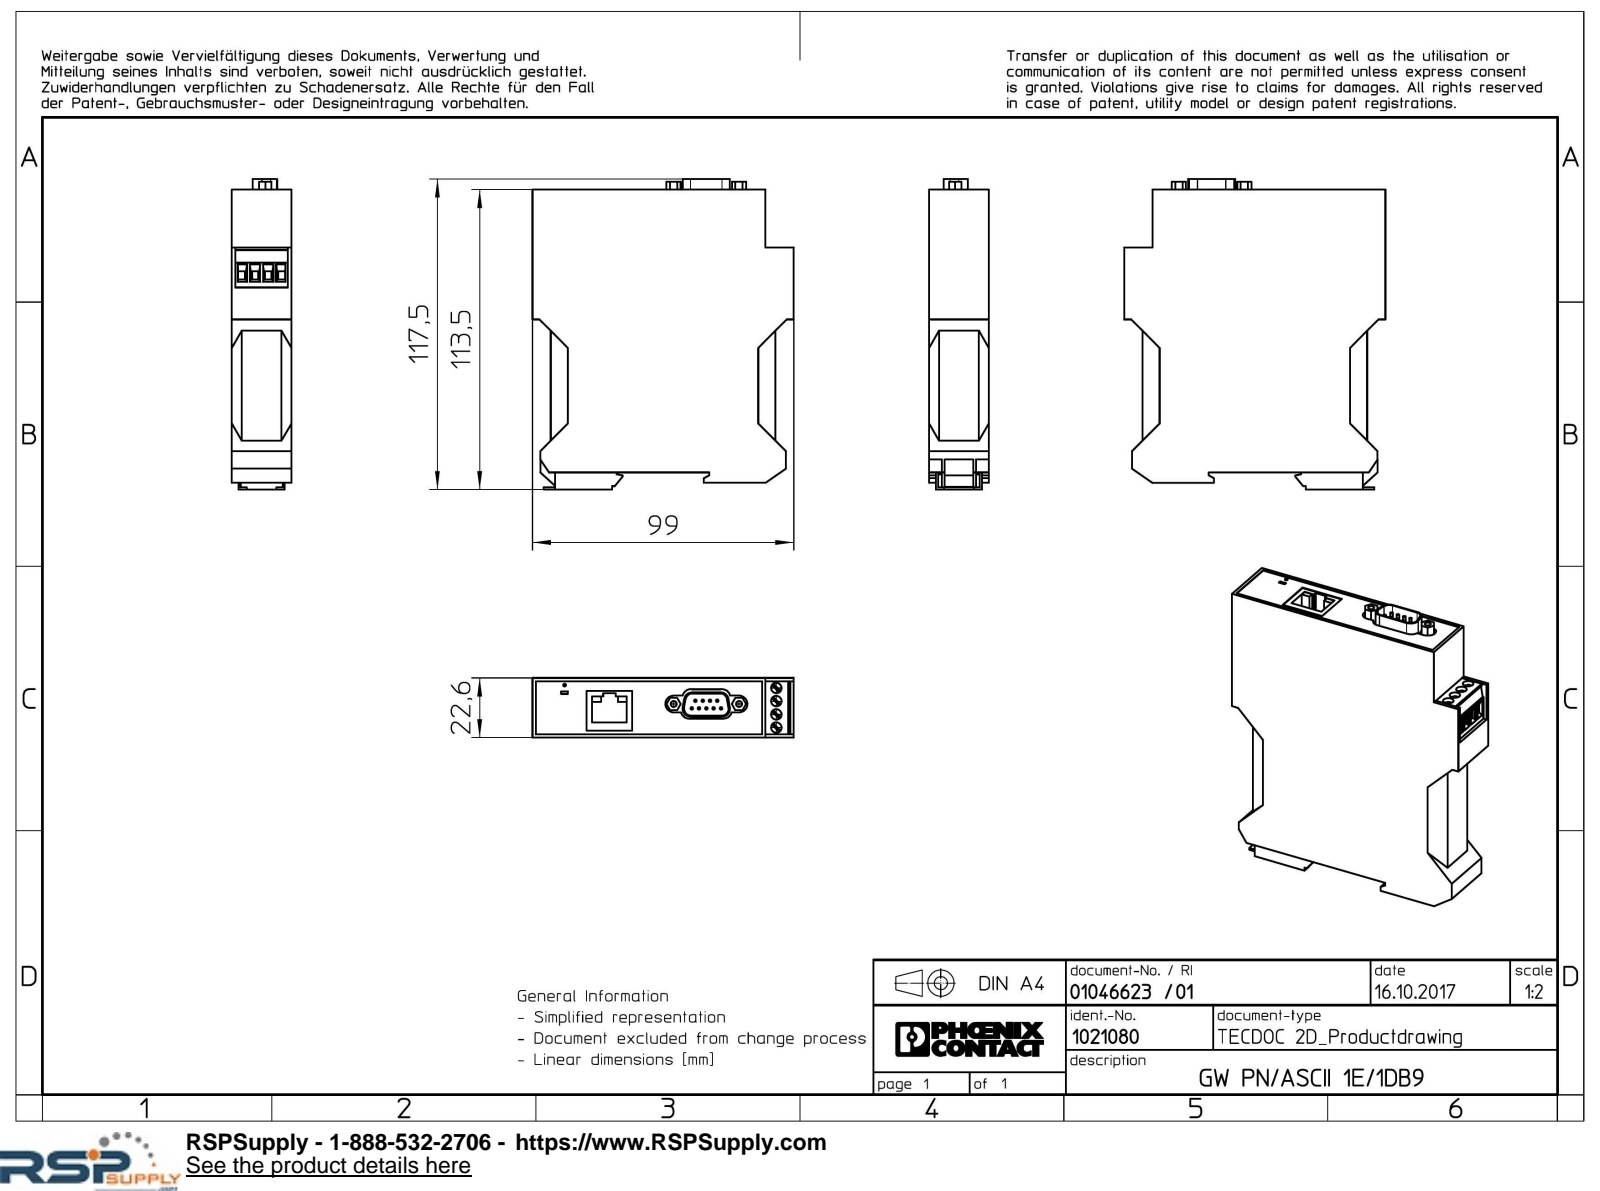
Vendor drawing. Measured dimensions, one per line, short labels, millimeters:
name: GW...ASCII_1E_1DB9-select
written by: Creo Elements/Direct Modeling 20.1A 29-Sep-2018 (C) Parametric Technology GmbH (AUTOMOTIVE_DESIGN)
unit: mm
bodies: 1 solid, 284 faces (238 planar, 46 cylindrical, 0 other)
size: 117.5 × 99 × 22.6
volume: 217 974 mm³; area: 31 622 mm²
holes: 4× ⌀4, 2× ⌀2.29, 1× ⌀1.08
bosses: 9× ⌀1
rounds: 6× R3.17, 4× R2.54, 4× R3.04
face distances: 22.6, 92.05, 4, 6.95, 106.8, 110.8, 85.1, 88.3, 81.35, 3.75
hole spacings: 5, 10, 14.18, 14.68, 15, 15.39, 16.72, 24.74
